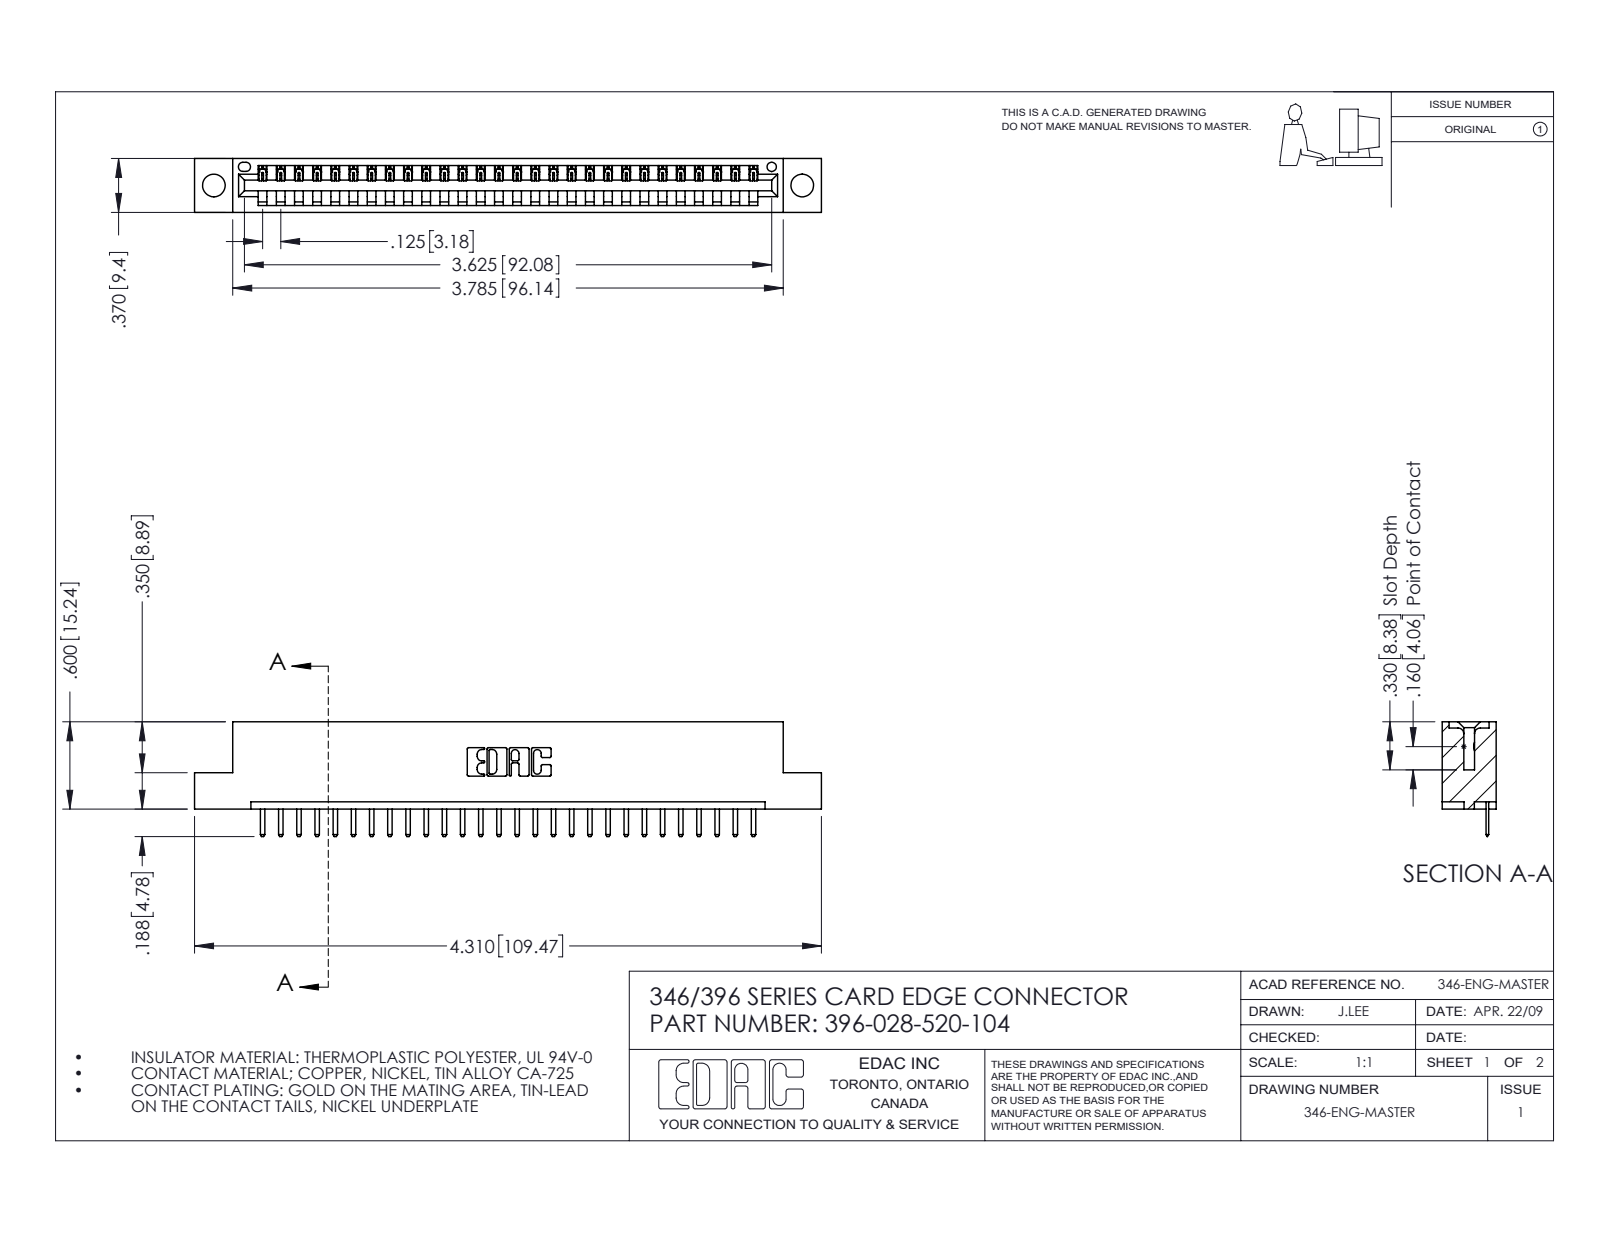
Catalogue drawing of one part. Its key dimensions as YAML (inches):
part_name: "396-028-520-104; 345-292-001_345-293-120; 346 Part_Flush Mounting Lugs - 0.156 Dia-TH"
step_written_by: "SolidWorks 2016 (CONFIG_CONTROL_DESIGN)"
units: inches
bodies: {solids: 29, faces: 1858, planar: 1252, cylindrical: 606, other: 0}
overall_size: [4.31, 0.788, 0.37]
volume: 0.623
surface_area: 18.83
round_holes:
  - {diameter: 0.156, count: 2}
  - {diameter: 0.064, count: 1}
partial_cylinders:
  - {radius: 0.01, count: 58}
  - {radius: 0.006, count: 56}
  - {radius: 0.01, count: 22}
  - {radius: 0.007, count: 6}
  - {radius: 0.031, count: 6}
  - {radius: 0.026, count: 3}
  - {radius: 0.031, count: 2}
  - {radius: 0.04, count: 2}
face_to_face_distances: [0.048, 0.322, 0.37, 0.25, 0.148, 0.222, 0.1, 0.174, 0.072, 0.298]
hole_center_spacings: [0.246, 3.837, 4.045]
